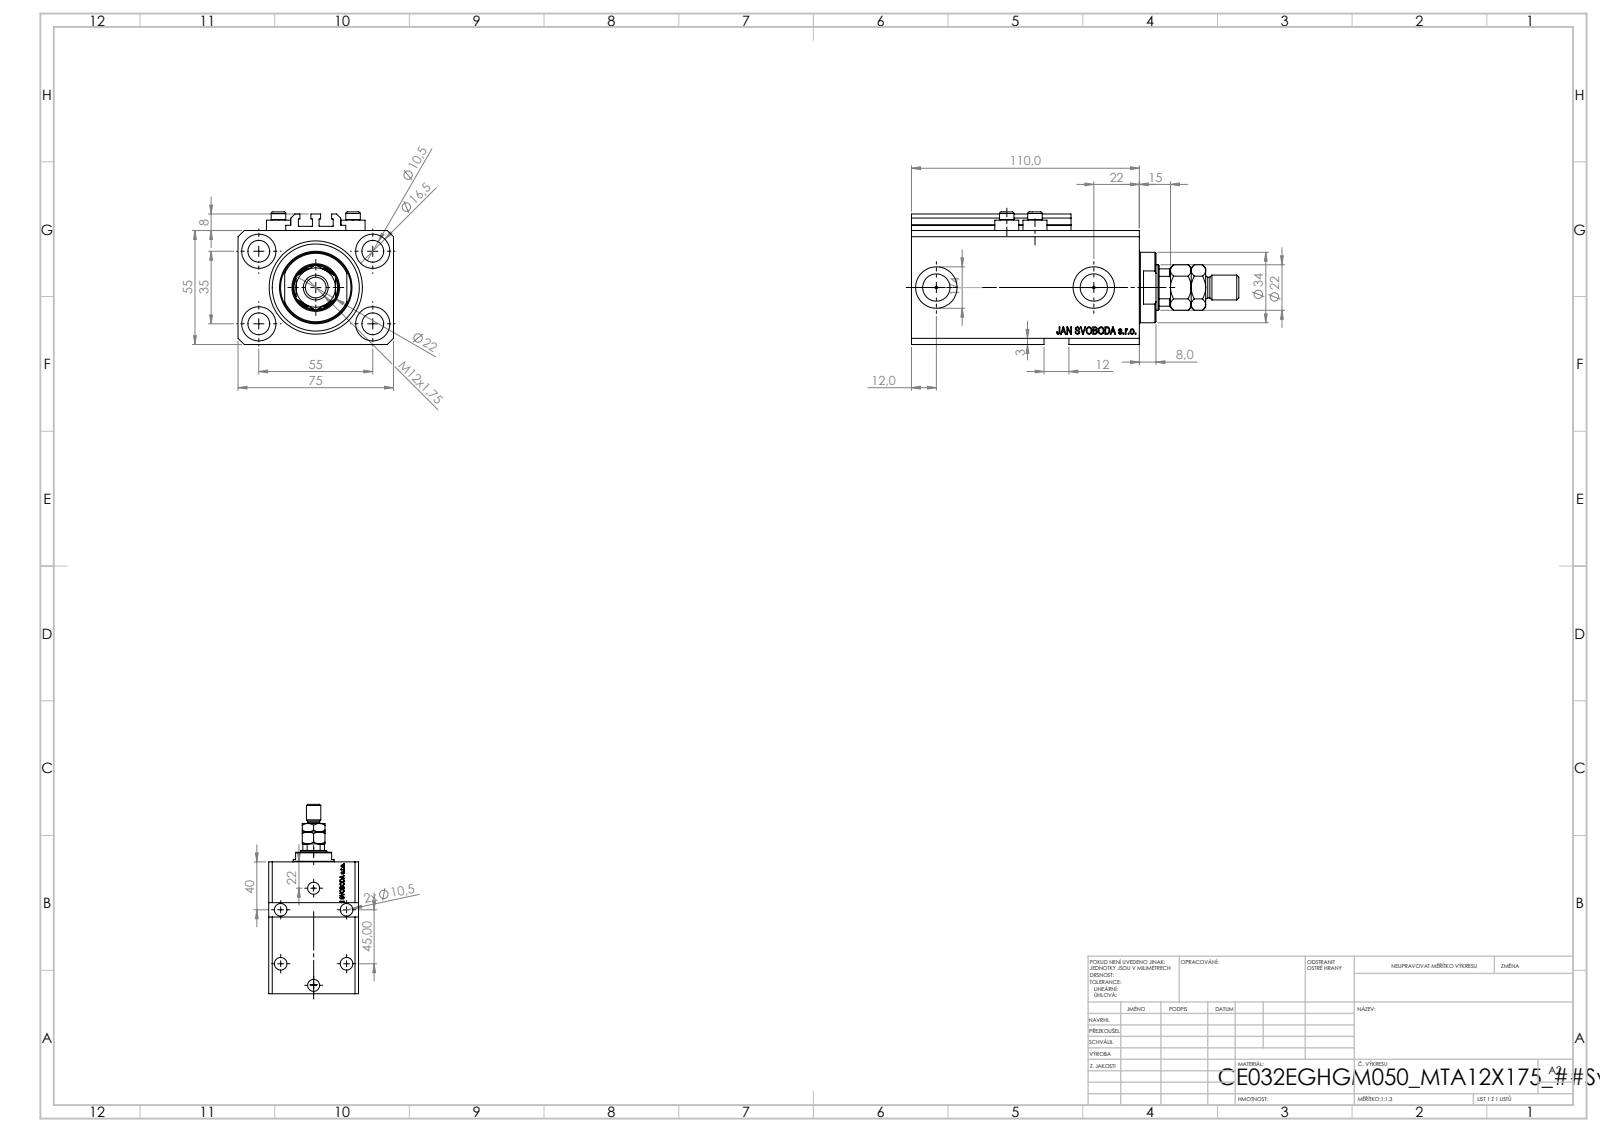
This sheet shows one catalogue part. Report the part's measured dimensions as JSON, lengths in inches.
{"part_name": "V250CE_C_VCP; V250CE_VC_E; V250CE_E_Body; MTA (+1 more)", "step_written_by": "SolidWorks 2019 (CONFIG_CONTROL_DESIGN)", "units": "inches", "bodies": {"solids": 9, "faces": 1133, "planar": 529, "cylindrical": 150, "other": 454}, "overall_size": [6.22, 2.953, 2.52], "volume_in3": 23.7, "surface_area_in2": 151.8, "round_holes": [[0.413, 9], [0.049, 4], [0.157, 4], [0.65, 4], [0.394, 2], [0.518, 2], [0.787, 2], [0.866, 1], [1.26, 1], [1.772, 1]], "round_bosses_or_shafts": [[0.457, 4], [0.276, 4], [1.339, 1], [0.472, 1], [0.394, 1]], "partial_cylinders_radius": [[0.008, 10], [0.413, 1]], "face_to_face_distances": [2.165, 2.953, 0.591, 4.331, 3.74, 0.118, 0.39, 3.35, 3.941, 0.098], "hole_center_spacings": [1.283, 1.294, 2.165, 2.706, 0.535, 0.555, 0.907, 1.016]}
